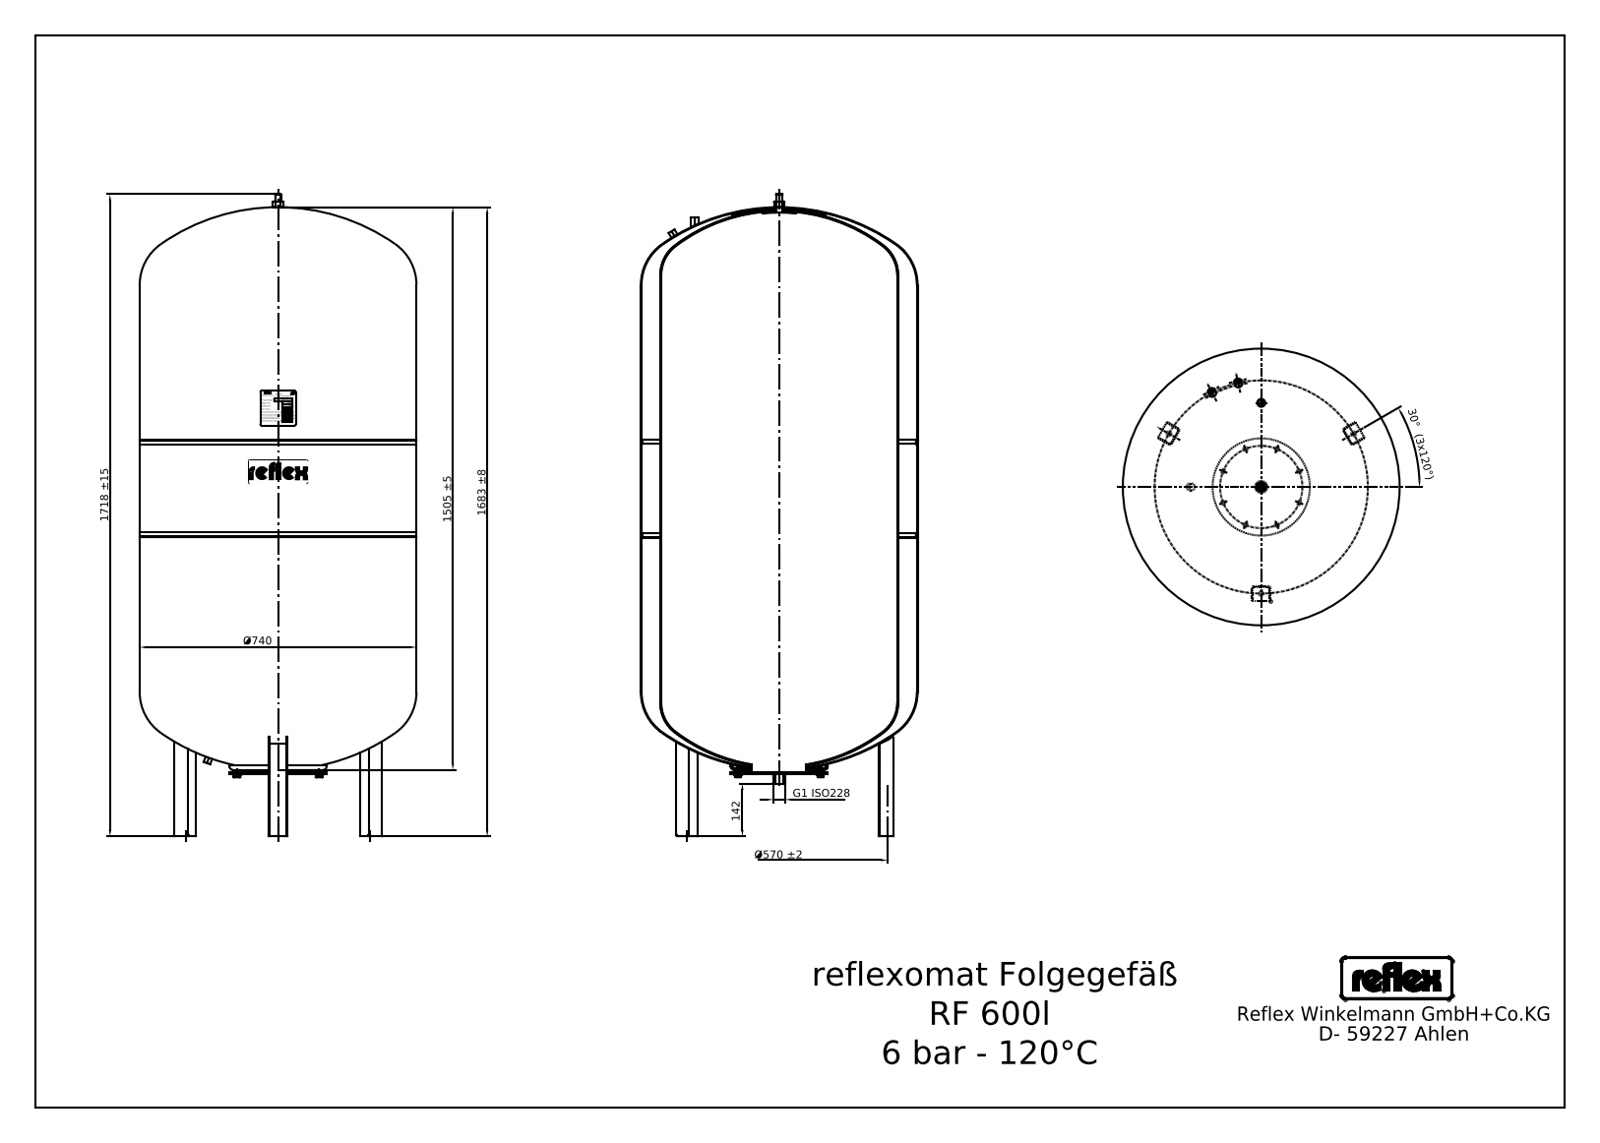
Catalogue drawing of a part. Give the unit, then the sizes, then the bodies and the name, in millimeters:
Units: millimetres
Overall size (bounding box): 1720 × 740 × 740
Round holes (diameter × count): ⌀11.45 ×2, ⌀14.95 ×1, ⌀161 ×1, ⌀250 ×1
Round bosses / shafts (diameter × count): ⌀10 ×8, ⌀21.3 ×2, ⌀18.5 ×2, ⌀740 ×1, ⌀260 ×1, ⌀230 ×1, ⌀34 ×1, ⌀33.7 ×1
Partial cylindrical surfaces — rounded edges, fillets, slot ends (radius × count): R25 ×18, R1 ×5, R3.94 ×4, R1.57 ×3, R9 ×3, R2.69 ×2, R4.72 ×2, R6.49 ×2
Main face-to-face distances: 1127, 6, 198, 1325, 204, 1331, 165, 5.88, 5, 17.75
Hole centre spacings: 225
Volume: 593 700 000 mm³ · Surface area: 6 253 000 mm²
Bodies: 18 solids, 450 faces (233 planar, 132 cylindrical, 85 other)
STEP written by: Mechanical Desktop 2008 (CONFIG_CONTROL_DESIGN)
